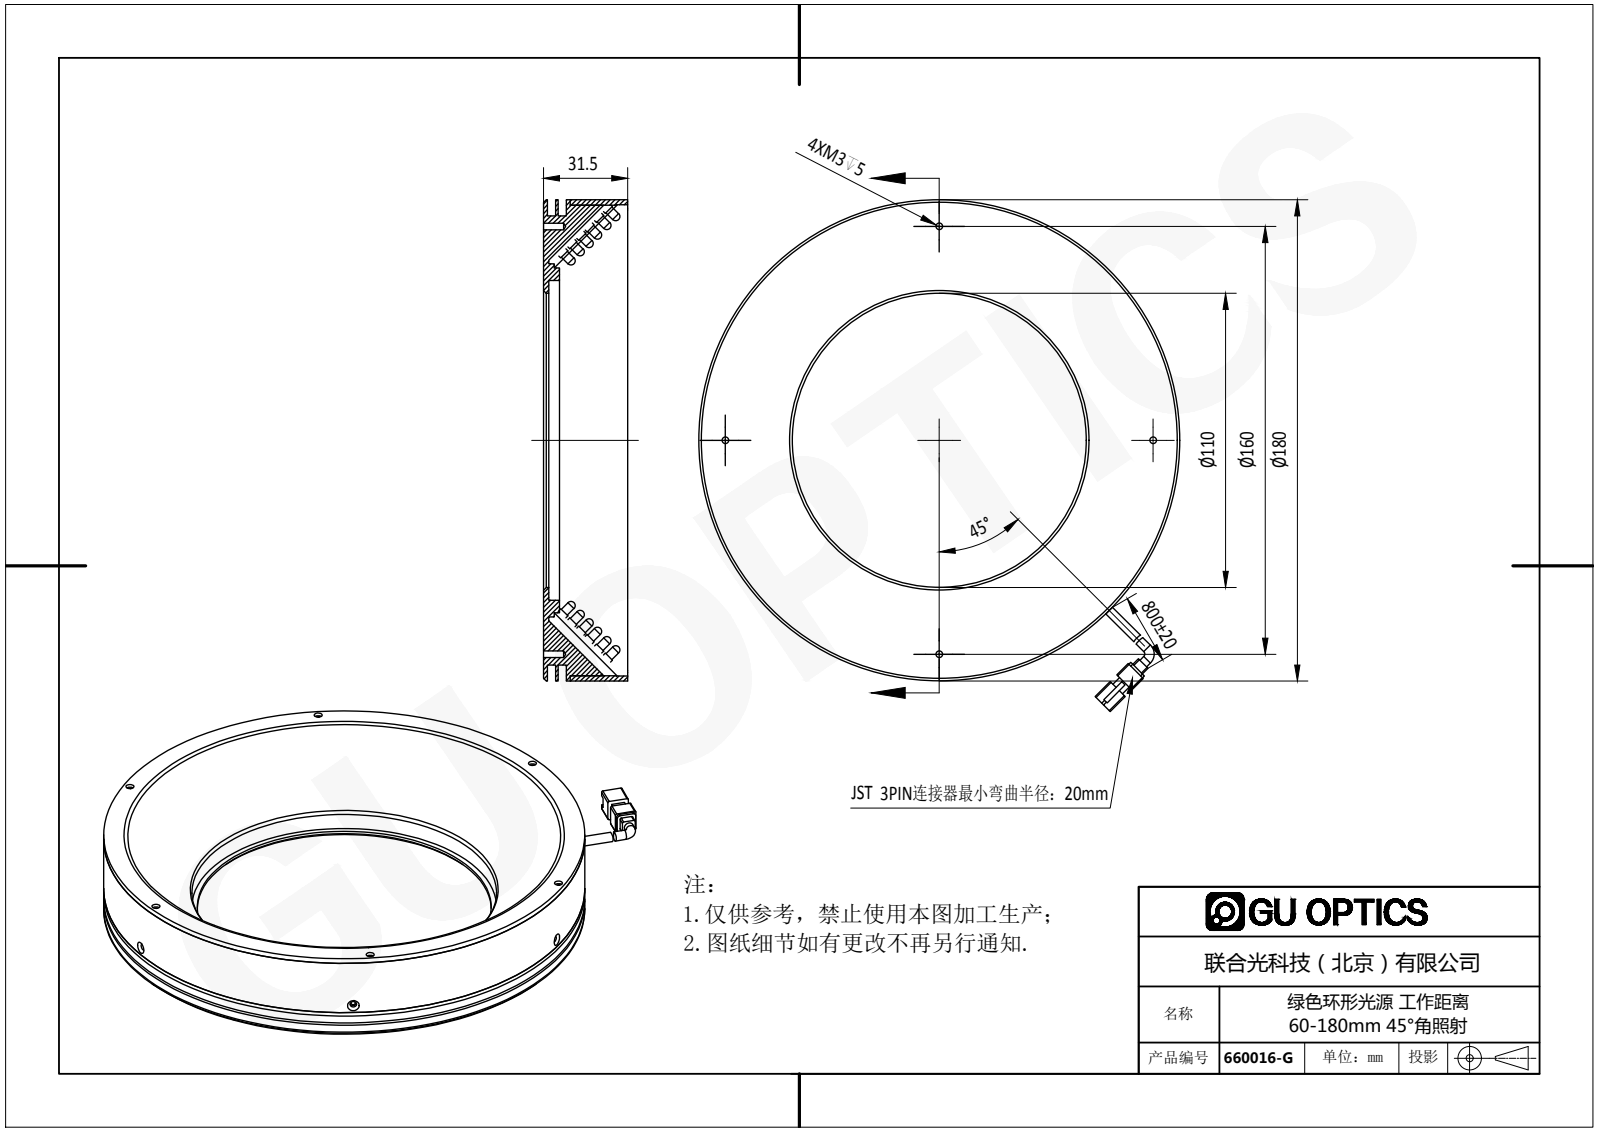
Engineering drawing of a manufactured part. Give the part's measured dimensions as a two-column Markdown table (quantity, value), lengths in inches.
| quantity | value |
| --- | --- |
| part name | 660016-G |
| STEP written by | SolidWorks 2016 (AUTOMOTIVE_DESIGN) |
| units | inches |
| bodies | 546 solids, 9482 faces (6561 planar, 2312 cylindrical, 609 other) |
| overall size | 7.538 × 7.087 × 1.319 |
| volume | 14.45 in³ |
| surface area | 336.4 in² |
| round holes (diameter × count) | 0.138 × 7, 0.049 × 6, 0.059 × 6, 0.118 × 6, 0.063 × 4, 0.098 × 4, 0.094 × 3, 4.331 × 1, 4.488 × 1, 4.709 × 1, 6.787 × 1 |
| round bosses / shafts (diameter × count) | 0.15 × 540, 0.118 × 540, 0.138 × 2, 7.087 × 1, 6.929 × 1, 6.614 × 1, 5.197 × 1, 5.079 × 1 |
| partial cylindrical surfaces (radius × count) | 0.02 × 8, 0.039 × 4, 0.295 × 1 |
| main face-to-face distances | 0.157, 1.24, 0.079, 0.02, 0.059, 0.177, 0.118, 0.098, 0.217, 0.335 |
| hole center spacings | 3.445, 5.967, 1.538, 2.026, 5.047, 5.967, 6.585, 6.716 |
